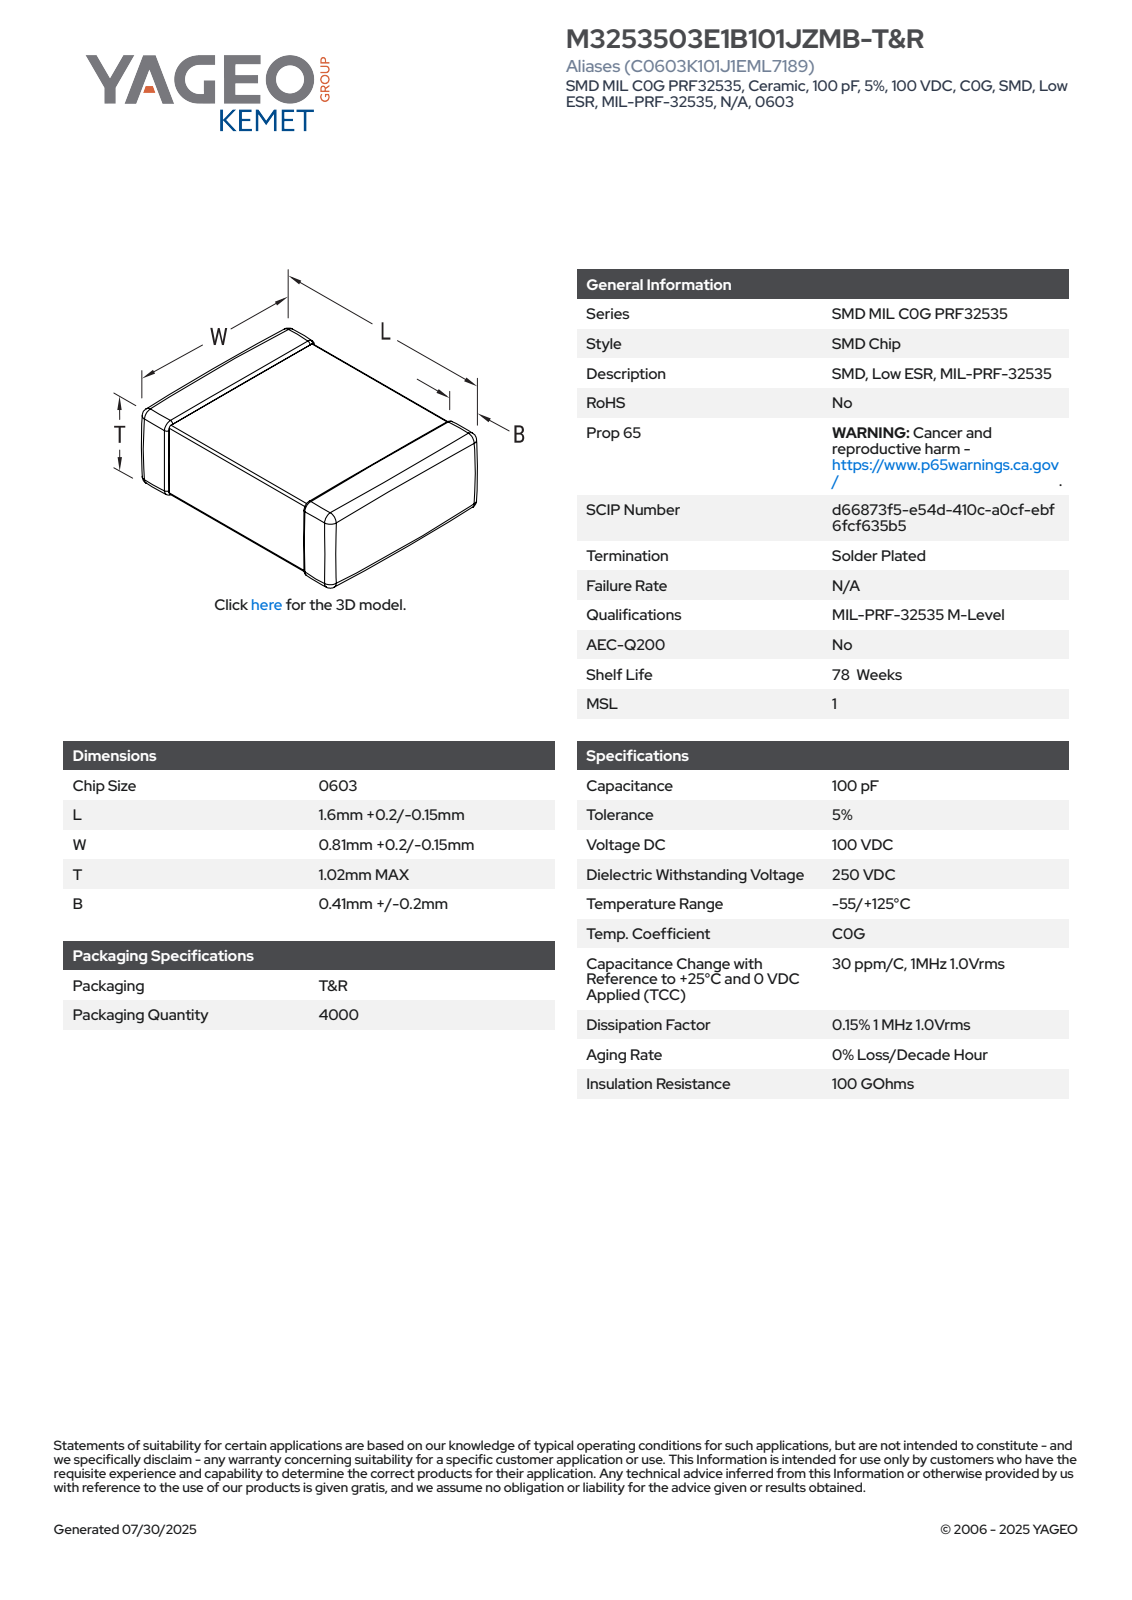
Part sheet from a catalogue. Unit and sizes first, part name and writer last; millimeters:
Units: millimetres
Overall size (bounding box): 1.8 × 1.02 × 1.01
Main face-to-face distances: 0.99, 1, 1.8, 0.97, 0.98, 1.01, 1.02, 0.56, 0.43, 0.45
Volume: 2 mm³ · Surface area: 9 mm²
Bodies: 4 solids, 125 faces (71 planar, 38 cylindrical, 16 other)
Part name (STEP PRODUCT): CCS_STDNOS_0603_L1.8W1.01T1.02B0.41
STEP written by: SolidWorks 2021 (AUTOMOTIVE_DESIGN)
